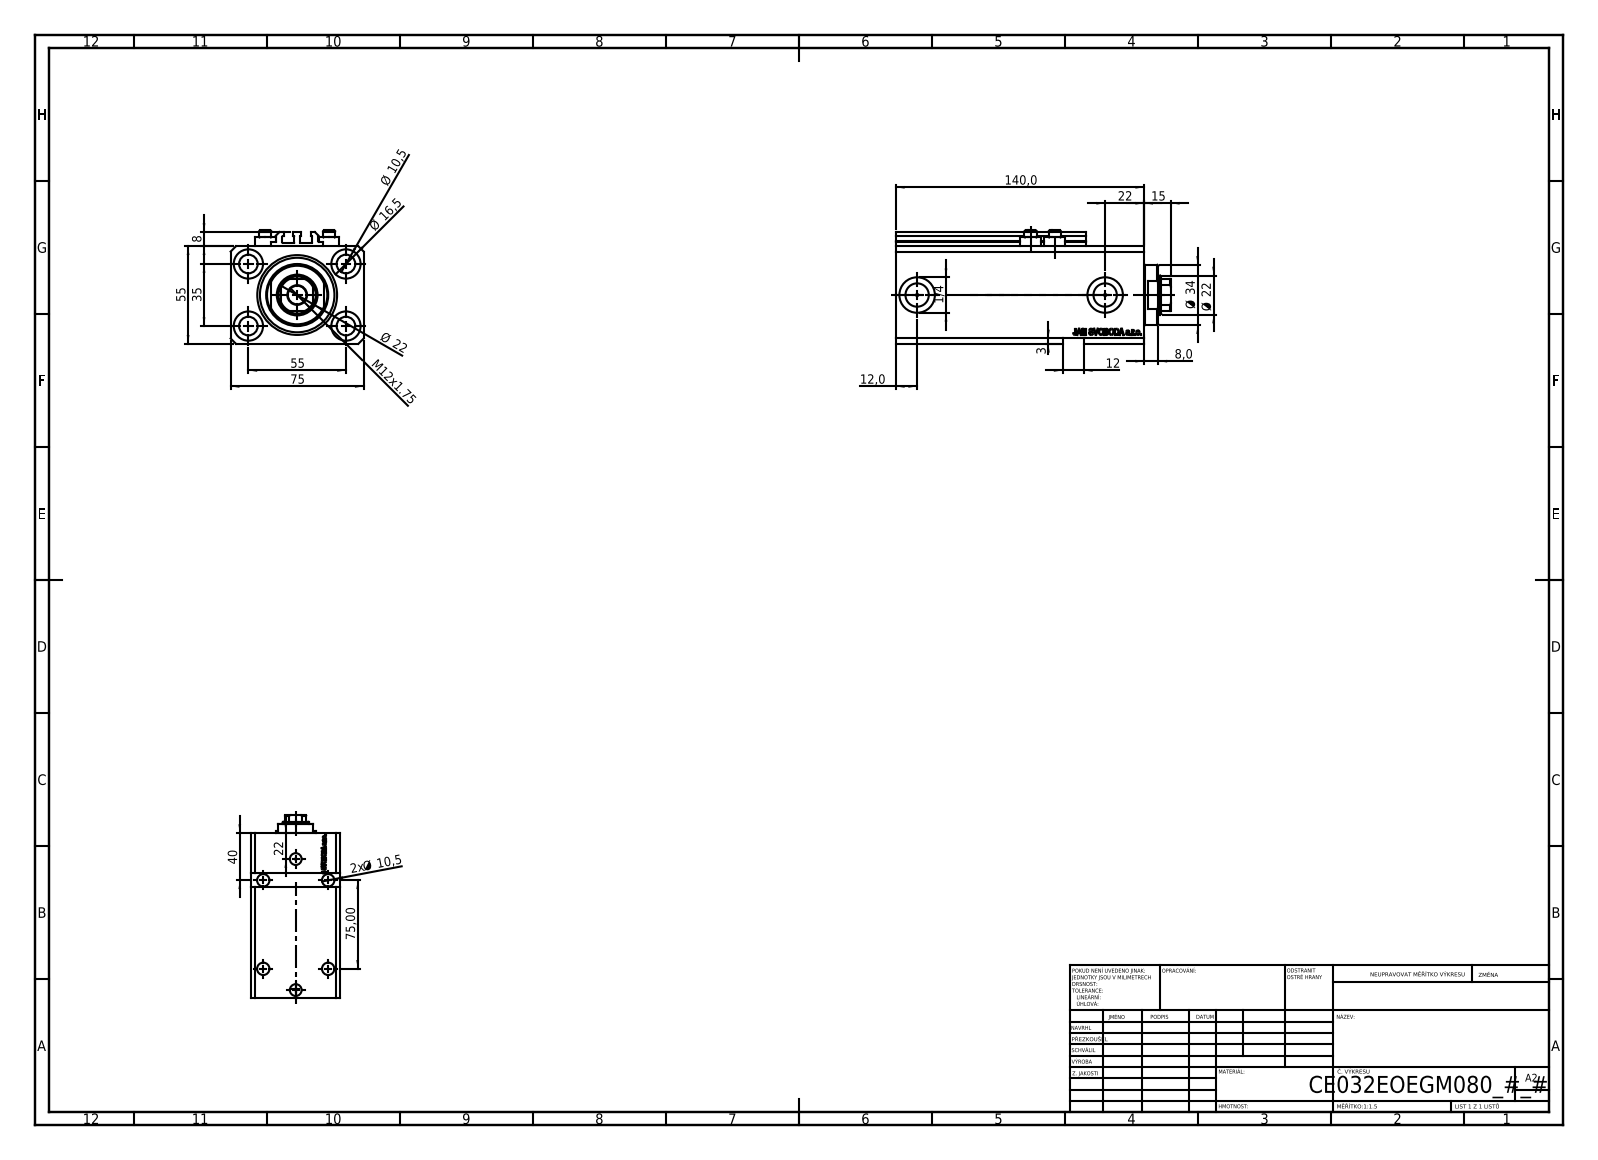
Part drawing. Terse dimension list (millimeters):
name: V250CE_VC_E; V250CE_C_VCP; ALLEN BOLT V250CE; V250CE_E_Body
written by: SolidWorks 2019 (CONFIG_CONTROL_DESIGN)
unit: mm
bodies: 8 solids, 1084 faces (514 planar, 146 cylindrical, 424 other)
size: 155 × 75 × 64
volume: 485 219 mm³; area: 115 303 mm²
holes: 9× ⌀10.5, 4× ⌀1.25, 4× ⌀4, 4× ⌀16.5, 2× ⌀10, 2× ⌀13.16, 2× ⌀20, 1× ⌀22, 1× ⌀32, 1× ⌀45
bosses: 4× ⌀11.6, 4× ⌀7, 1× ⌀34
rounds: 10× R0.2, 1× R10.5
face distances: 55, 75, 15, 140, 125, 3, 9.9, 57, 115.1, 130.1
hole spacings: 32.6, 32.87, 55, 96.98, 13.6, 14.09, 25.81, 32.58
